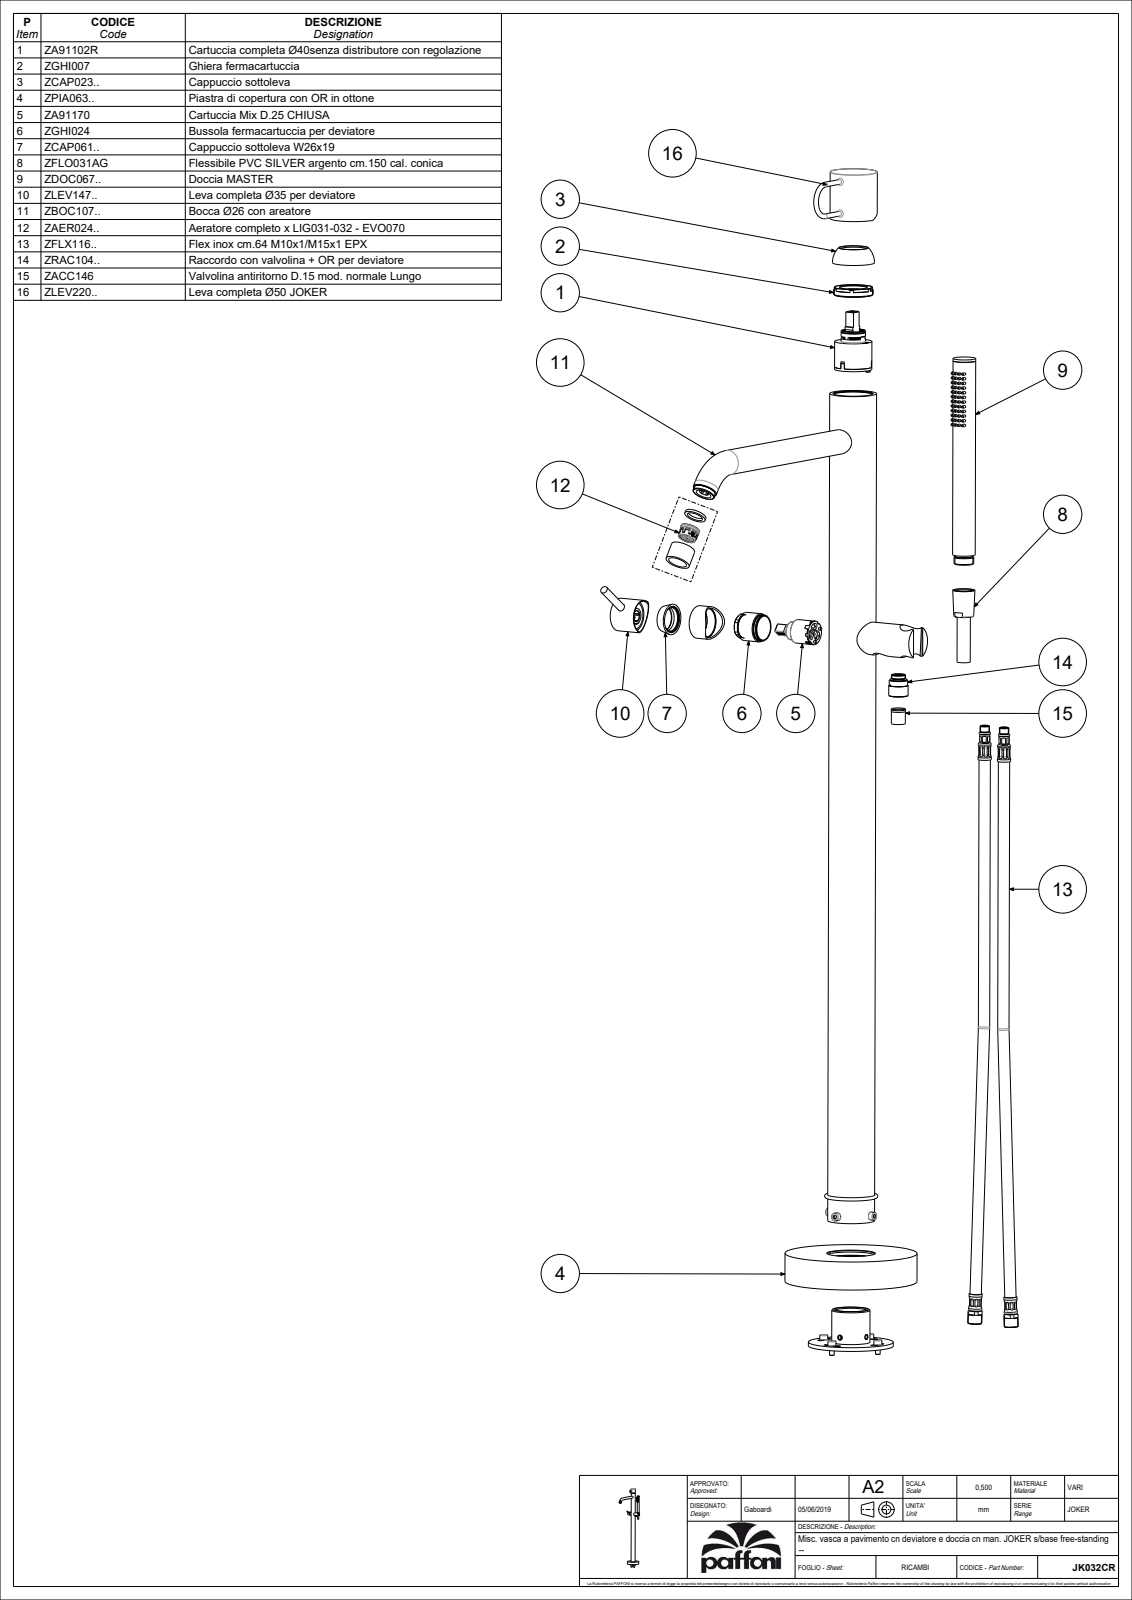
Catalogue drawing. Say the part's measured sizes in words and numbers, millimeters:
The part is named "JK032CR". Its 3-D file was written by "CREO PARAMETRIC BY PTC INC, 2020044 (CONFIG_CONTROL_DESIGN)". It is 24 solids with 618 faces: 229 planar, 207 cylindrical and 182 other. Overall it measures 937.74 by 364.39 by 158.99 millimeters. Its volume is 1 323 000 cubic millimeters and its surface area 394 345 square millimeters. Round holes: 50 of diameter 1, 2 of diameter 4.5, 2 of diameter 5.5, 2 of diameter 8, 1 of diameter 3, 1 of diameter 4.2, 1 of diameter 5, 1 of diameter 10, 1 of diameter 11, 1 of diameter 14.5, 1 of diameter 18.5, 1 of diameter 20. Round bosses or shafts: 2 of diameter 26, 2 of diameter 5, 1 of diameter 140, 1 of diameter 50, 1 of diameter 49.7, 1 of diameter 34.7, 1 of diameter 24, 1 of diameter 20.9. Partial cylindrical surfaces (rounded edges, fillets, slot ends): 1 of radius 24.77, 1 of radius 24.91. The main face-to-face distances are 30, 934.3, 904.3, 853, 823, 81.3, 3, 64.35, 74.45, 10.1. The hole center spacings are 6.4, 10.77, 15.52, 5, 10, 20.4, 15, 4.
